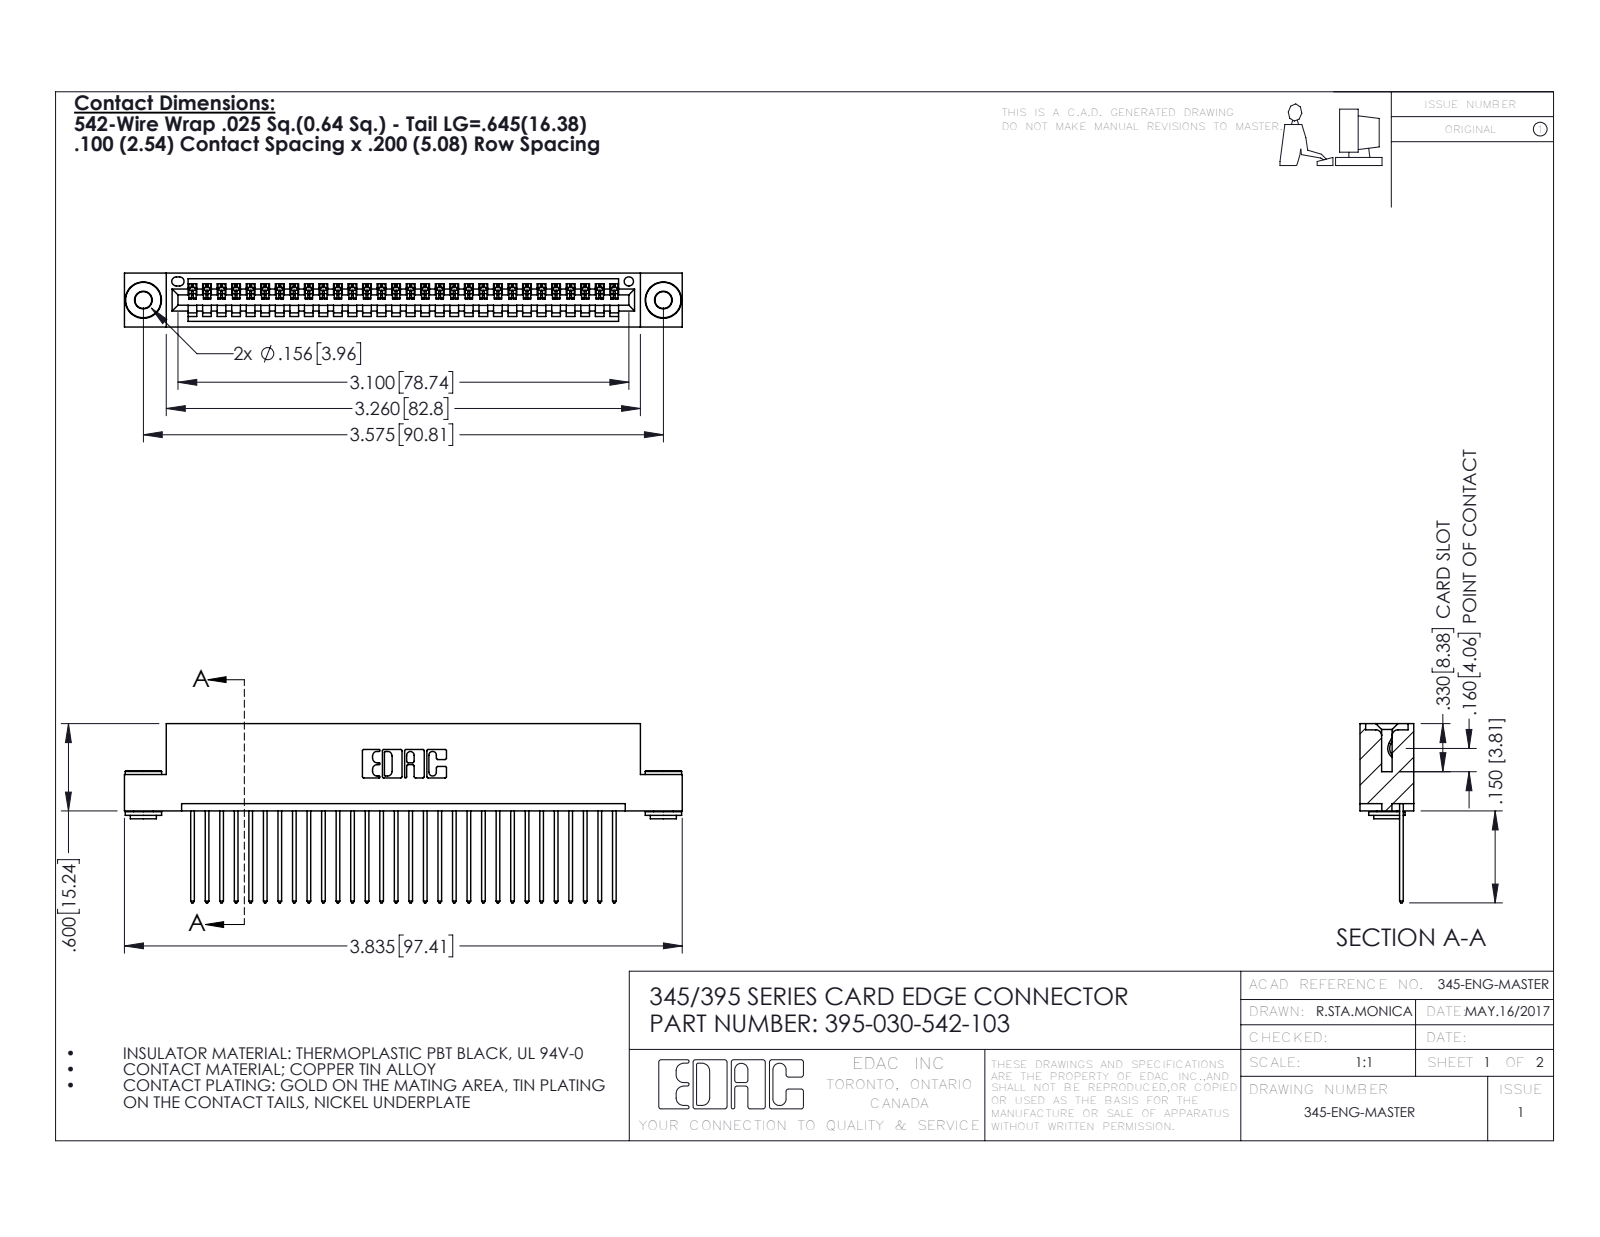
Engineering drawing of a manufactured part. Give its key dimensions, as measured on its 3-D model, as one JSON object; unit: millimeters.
{"part_name": "345 Part_Flush Mounting Lugs - 0.156 Dia-TH; 345-292-001_345-293-142; 345-250-002_345-250-002-102; 395-030-542-103", "step_written_by": "SolidWorks 2016 (CONFIG_CONTROL_DESIGN)", "units": "millimeters", "bodies": {"solids": 33, "faces": 1904, "planar": 1290, "cylindrical": 606, "other": 8}, "overall_size": [97.4, 31.3, 9.4], "volume_mm3": 9240, "surface_area_mm2": 12750, "round_holes": [[2.9, 2], [4, 2], [1.6, 1]], "round_bosses_or_shafts": [[6.4, 2], [4.6, 2], [3.5, 2]], "partial_cylinders_radius": [[0.2, 60], [0.3, 60], [0.3, 22], [0.2, 6], [0.8, 6], [0.7, 3], [0.8, 2], [1, 2]], "face_to_face_distances": [1.8, 7.6, 5.1, 9.4, 0.6, 2.5, 6.9, 5.7, 3.8, 1.8], "hole_center_spacings": [6.9, 84.8, 90.8]}
